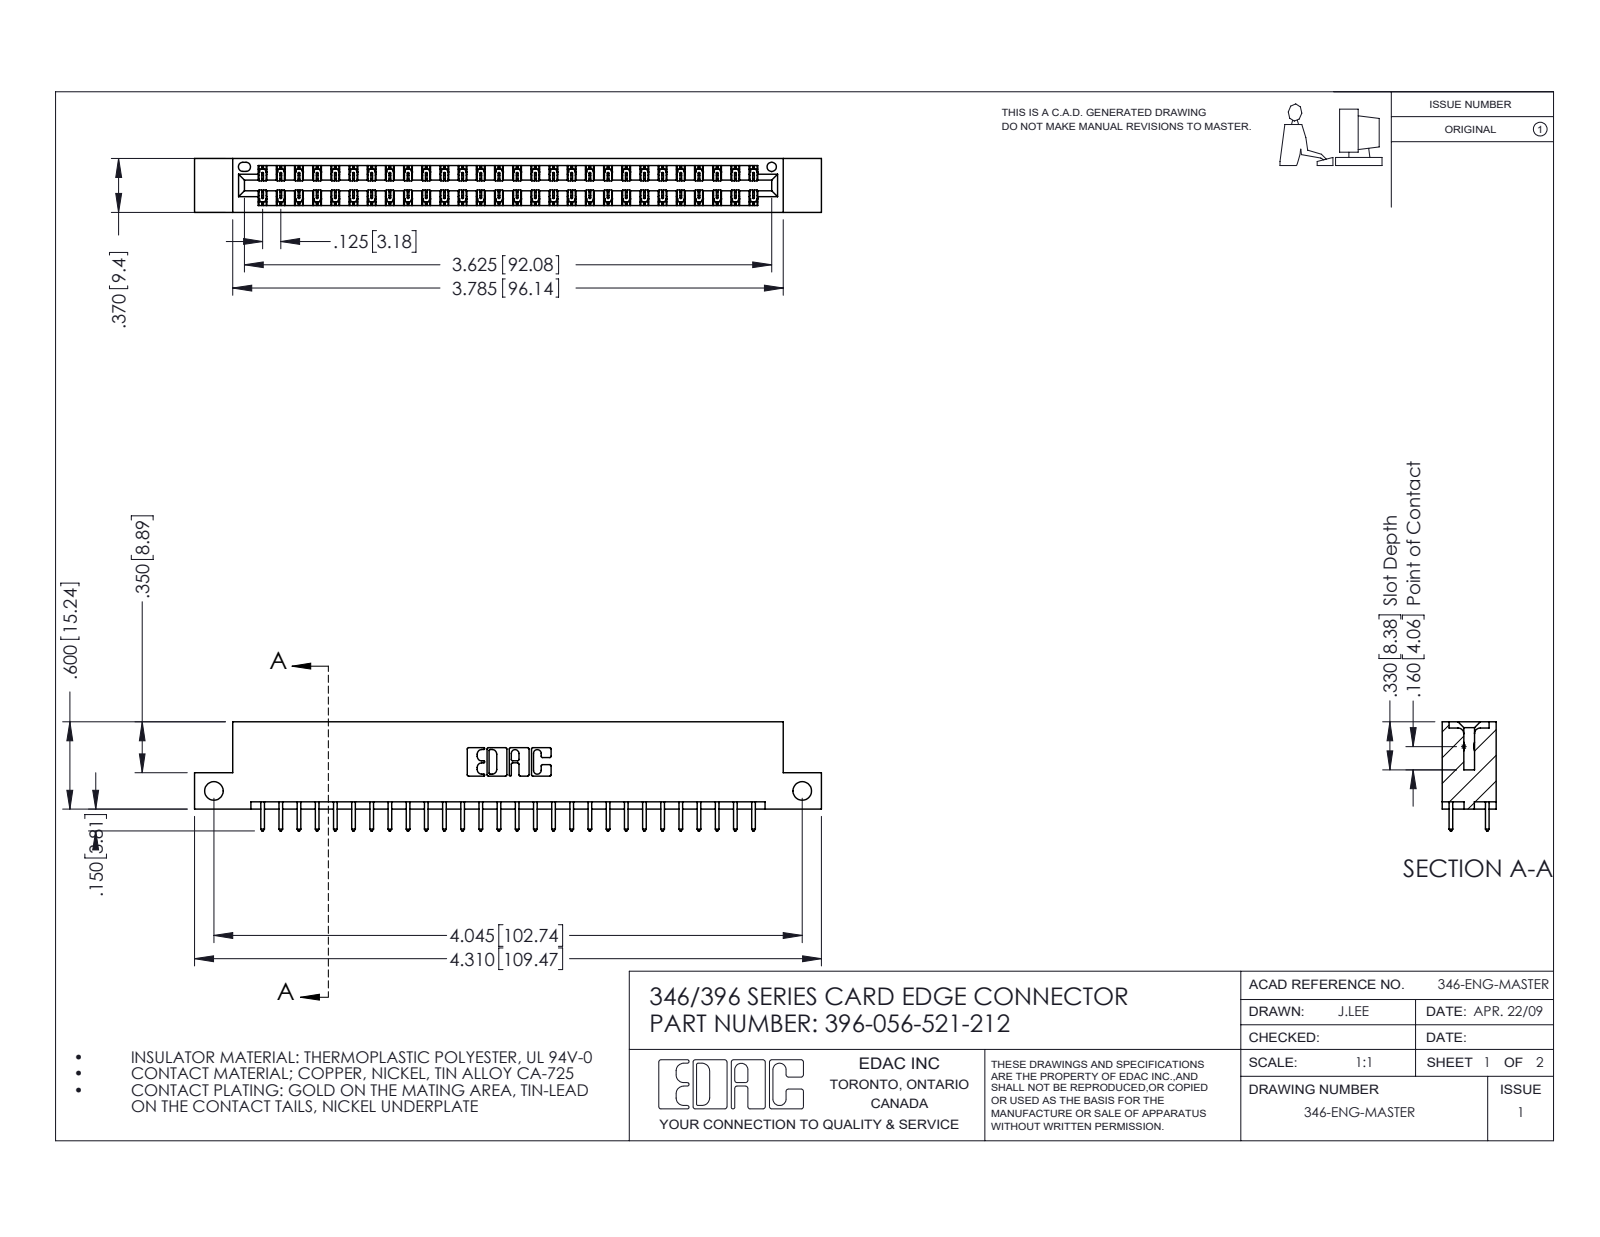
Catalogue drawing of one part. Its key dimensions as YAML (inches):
part_name: "396-056-521-212; 346 Part_Flush Mounting Lugs - Side Mount; 345-292-001_345-293-121"
step_written_by: "SolidWorks 2016 (CONFIG_CONTROL_DESIGN)"
units: inches
bodies: {solids: 57, faces: 3034, planar: 2036, cylindrical: 998, other: 0}
overall_size: [4.31, 0.75, 0.37]
volume: 0.638
surface_area: 21.49
round_holes:
  - {diameter: 0.128, count: 2}
  - {diameter: 0.064, count: 1}
partial_cylinders:
  - {radius: 0.006, count: 84}
  - {radius: 0.01, count: 56}
  - {radius: 0.01, count: 22}
  - {radius: 0.007, count: 6}
  - {radius: 0.031, count: 6}
  - {radius: 0.026, count: 3}
  - {radius: 0.014, count: 2}
  - {radius: 0.022, count: 2}
face_to_face_distances: [0.048, 0.322, 0.25, 0.37, 0.072, 0.298, 0.025, 0.275, 0.148, 0.222]
hole_center_spacings: [4.045]
